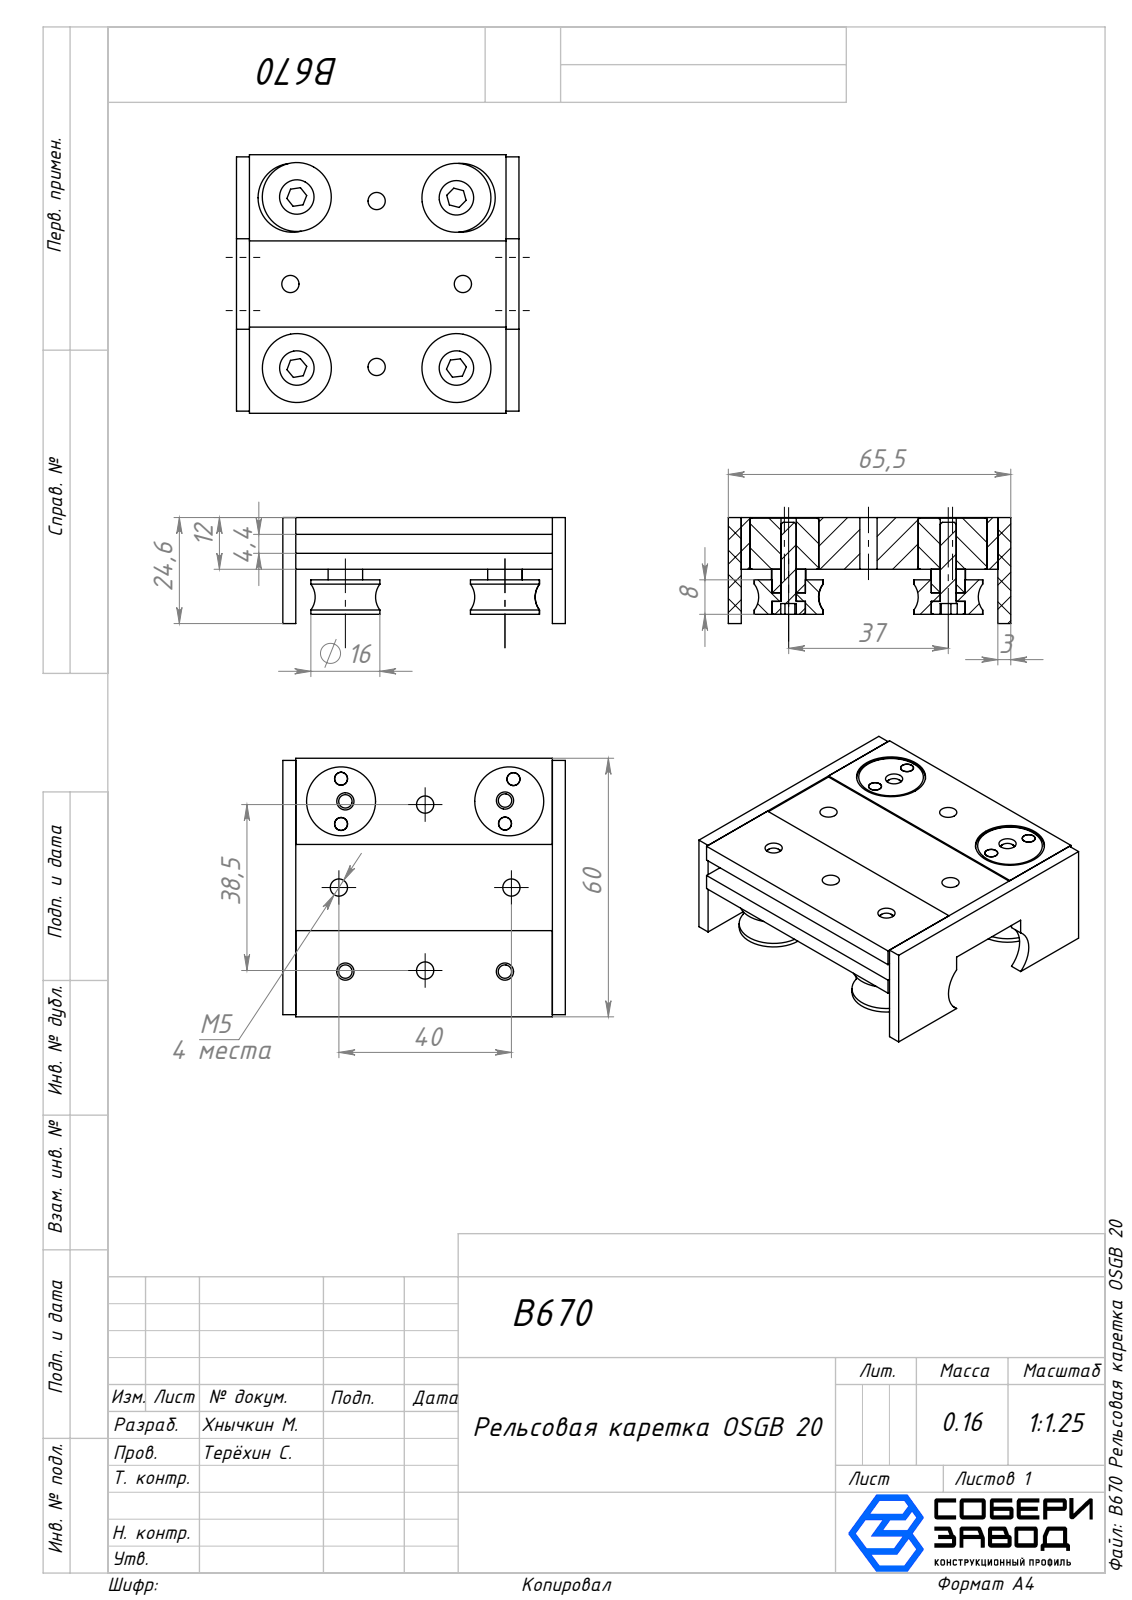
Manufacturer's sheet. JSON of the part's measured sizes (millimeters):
{"part_name": "B670 Рельсовая каретка OSGB 20; B670 Ролик_00; B670 Дистанционная втулка_00; B670 Заслонка_00 (+2 more)", "step_written_by": "SolidWorks 2025 (AUTOMOTIVE_DESIGN)", "units": "millimeters", "bodies": {"solids": 17, "faces": 200, "planar": 74, "cylindrical": 102, "other": 24}, "overall_size": [65.5, 60, 24.6], "volume_mm3": 50793, "surface_area_mm2": 25631, "round_holes": [[4, 8], [3, 4], [8, 4], [16, 2]], "round_bosses_or_shafts": [[16, 4]], "partial_cylinders_radius": [[7, 2]], "face_to_face_distances": [3, 11.7, 12, 62.5, 59.5, 11.4, 65.5, 14.15, 8, 2.45], "hole_center_spacings": [5.25, 27.76, 5.34, 1, 18.5, 19.51, 19.56, 20.01]}
